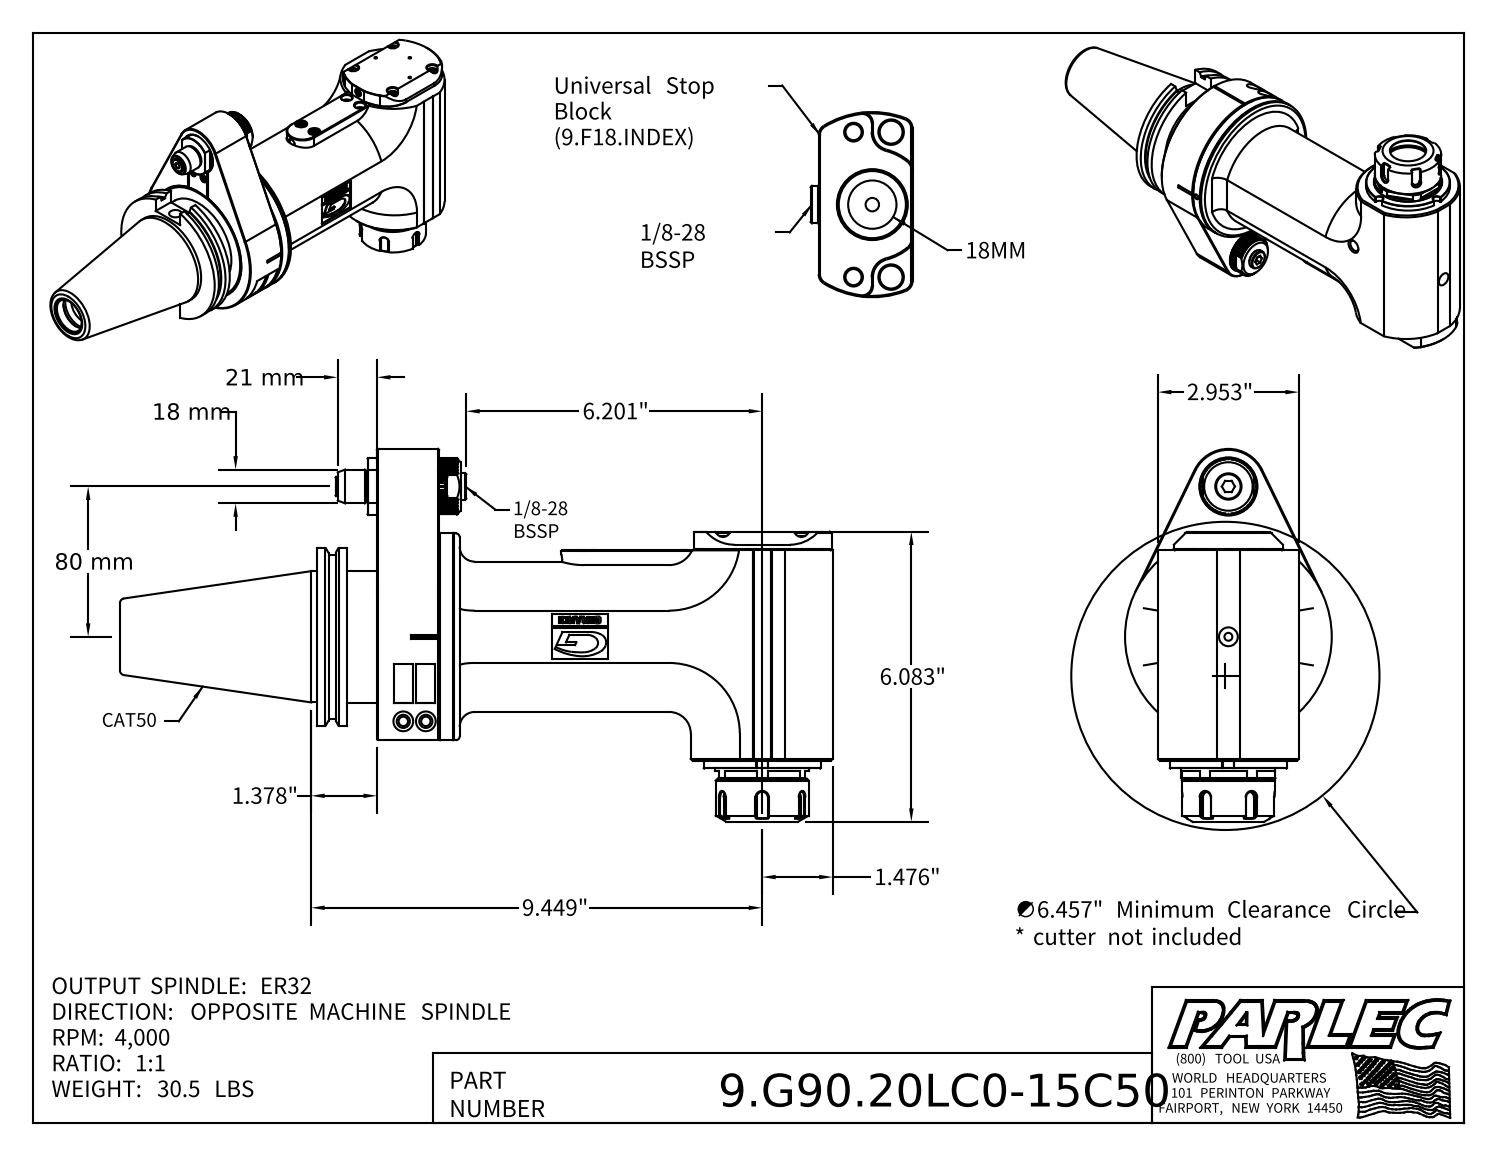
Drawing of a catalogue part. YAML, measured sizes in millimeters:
part_name: "9.G90.20LC0-15C50; 9_GA2_458_1 (Classic, Type 2, Cat50, 80mm); G90-20LC"
step_written_by: "Autodesk Inventor 2022 (AUTOMOTIVE_DESIGN)"
units: millimeters
bodies: {solids: 4, faces: 1042, planar: 545, cylindrical: 218, other: 279}
overall_size: [379.3, 198.5, 110]
volume: 2098000
surface_area: 225600
round_holes:
  - {diameter: 5, count: 15}
  - {diameter: 8, count: 8}
  - {diameter: 8.5, count: 4}
  - {diameter: 2, count: 3}
  - {diameter: 3.3, count: 3}
  - {diameter: 4, count: 2}
  - {diameter: 4.2, count: 2}
  - {diameter: 4.5, count: 2}
  - {diameter: 6, count: 2}
  - {diameter: 7, count: 2}
  - {diameter: 10.5, count: 2}
  - {diameter: 11, count: 2}
round_bosses_or_shafts:
  - {diameter: 7, count: 6}
  - {diameter: 10, count: 2}
  - {diameter: 110, count: 1}
  - {diameter: 102, count: 1}
  - {diameter: 98.4, count: 1}
  - {diameter: 91.3, count: 1}
  - {diameter: 89.5, count: 1}
  - {diameter: 80, count: 1}
partial_cylinders:
  - {radius: 3, count: 8}
  - {radius: 20, count: 5}
  - {radius: 2.2, count: 2}
  - {radius: 8, count: 2}
  - {radius: 11.9, count: 2}
  - {radius: 12, count: 2}
  - {radius: 39, count: 2}
  - {radius: 40, count: 2}
face_to_face_distances: [33, 8, 25, 15.9, 75, 23.9, 48.9, 5, 3, 64.8]
hole_center_spacings: [47.5, 21.1, 44.1, 24.6, 29.5, 41.7, 67.2, 82.3]
